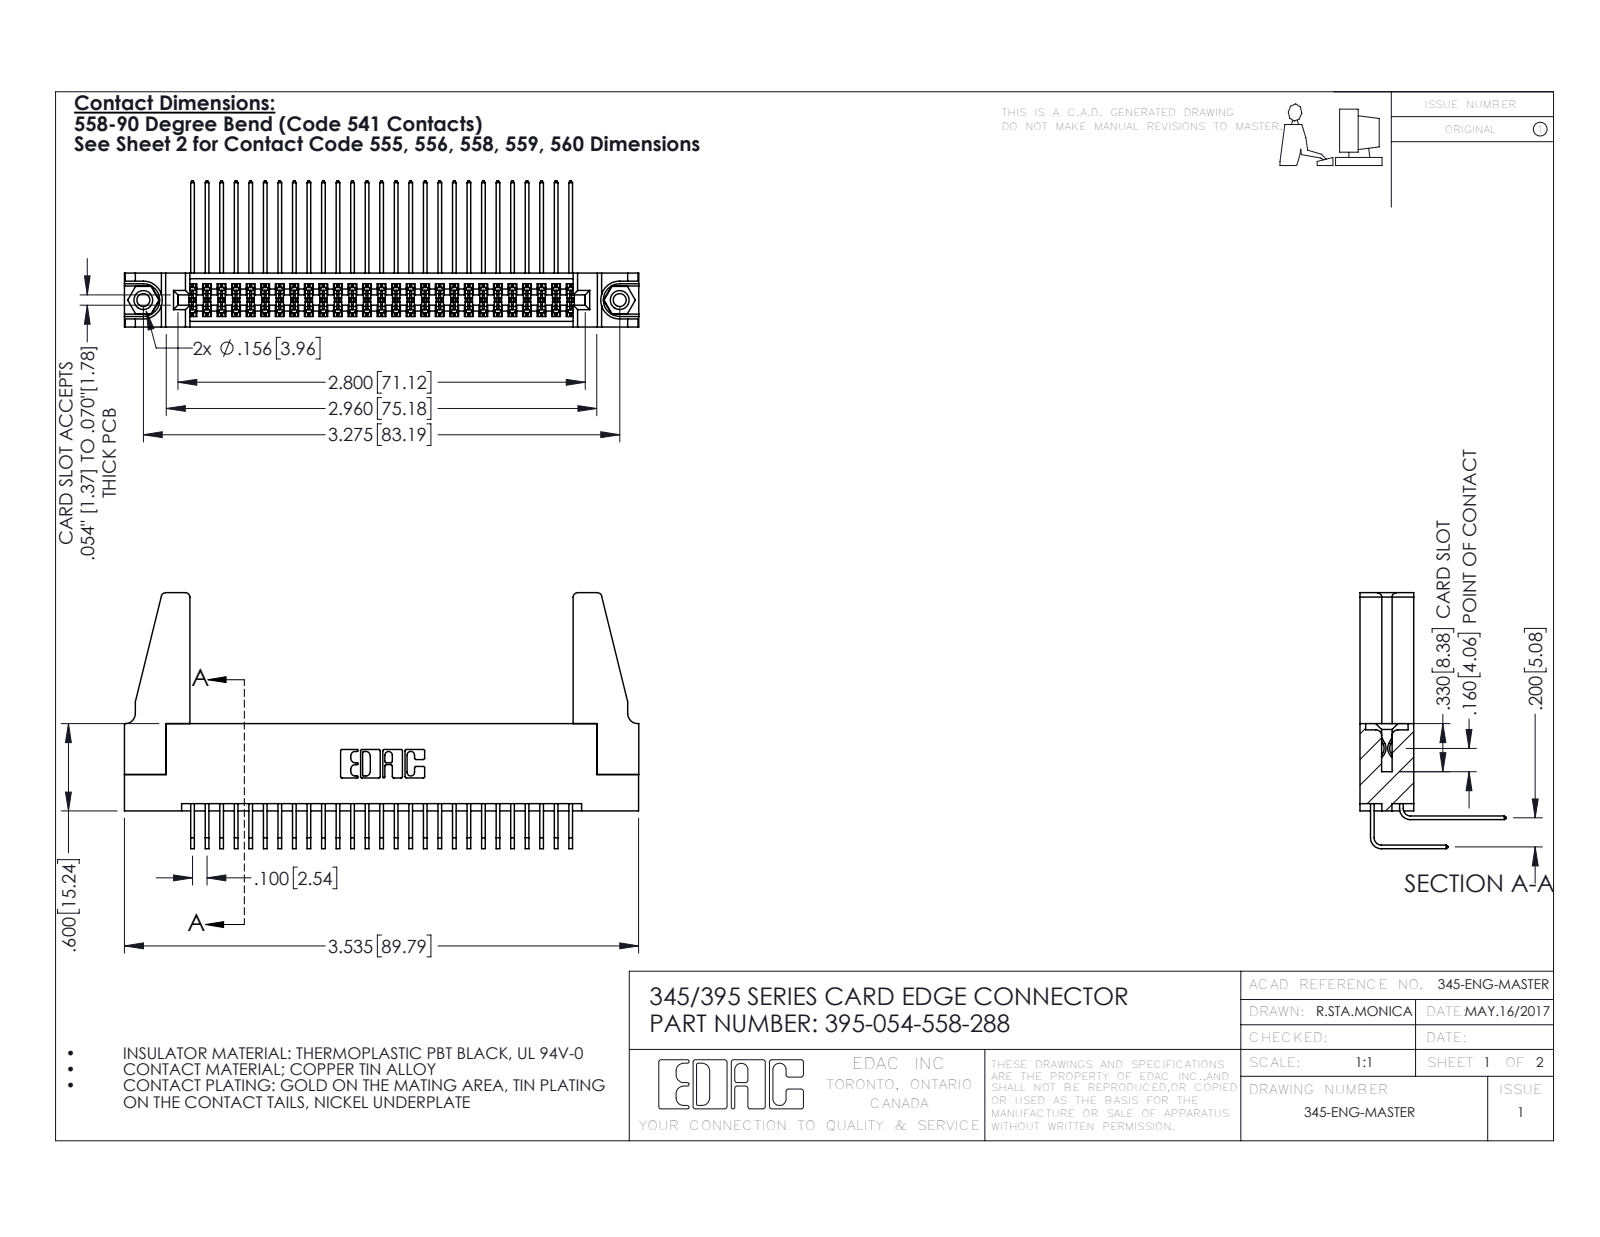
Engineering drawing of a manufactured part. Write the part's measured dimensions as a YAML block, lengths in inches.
part_name: "345-250-001_345-250-001-102; 345-220-078_345-220-088; 345 Part_Flush Mounting Lugs - 0.156 Dia-TH; 345-292-001_558 Tail - 2 (+2 more)"
step_written_by: "SolidWorks 2016 (CONFIG_CONTROL_DESIGN)"
units: inches
bodies: {solids: 59, faces: 3058, planar: 2042, cylindrical: 1000, other: 16}
overall_size: [3.536, 1.759, 1.005]
volume: 0.741
surface_area: 27.04
round_holes:
  - {diameter: 0.089, count: 2}
  - {diameter: 0.125, count: 2}
  - {diameter: 0.156, count: 2}
  - {diameter: 0.064, count: 1}
round_bosses_or_shafts:
  - {diameter: 0.155, count: 2}
partial_cylinders:
  - {radius: 0.006, count: 82}
  - {radius: 0.01, count: 22}
  - {radius: 0.03, count: 8}
  - {radius: 0.007, count: 6}
  - {radius: 0.031, count: 6}
  - {radius: 0.026, count: 3}
  - {radius: 0.014, count: 2}
  - {radius: 0.019, count: 2}
face_to_face_distances: [0.072, 0.298, 0.2, 0.37, 0.098, 0.272, 0.025, 0.225, 0.285, 0.025]
hole_center_spacings: [0.27, 3.04, 3.275]
